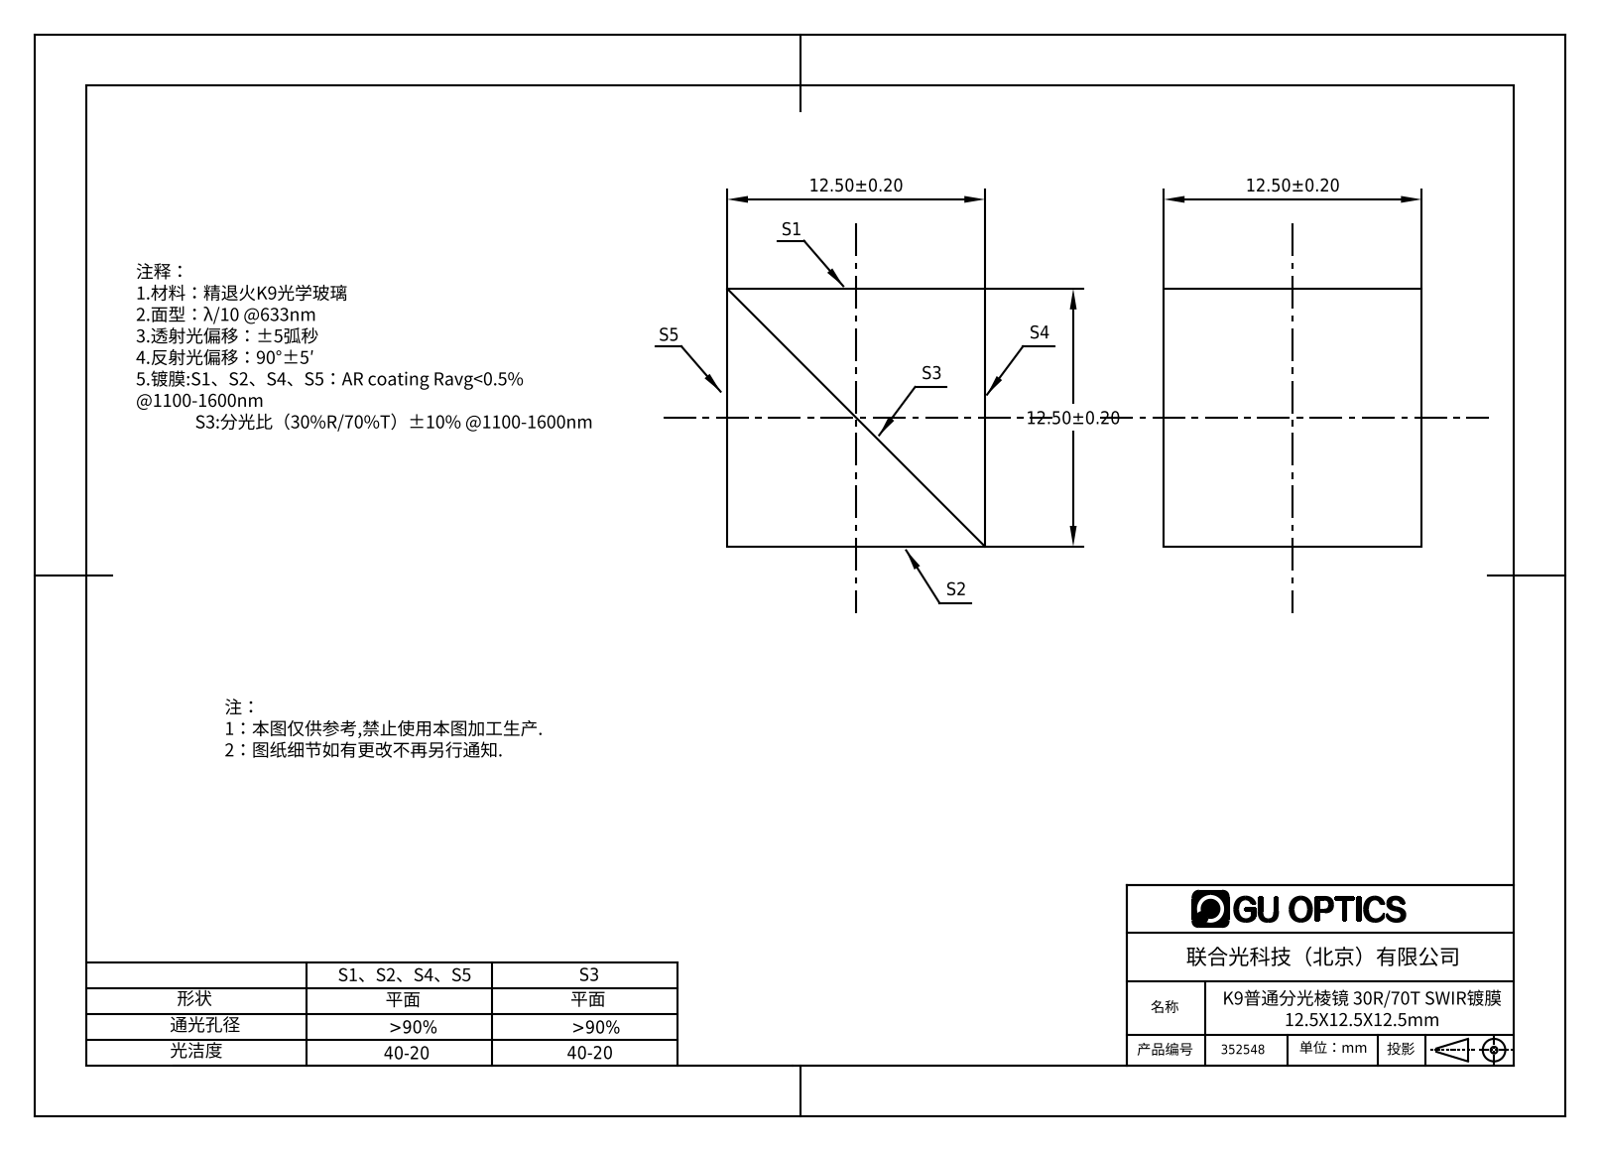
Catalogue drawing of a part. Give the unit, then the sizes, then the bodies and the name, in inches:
Units: inches
Overall size (bounding box): 0.492 × 0.492 × 0.492
Main face-to-face distances: 0.492
Volume: 0.119 in³ · Surface area: 2.137 in²
Bodies: 2 solids, 10 faces (10 planar, 0 cylindrical, 0 other)
Part name (STEP PRODUCT): 352506
STEP written by: SolidWorks 2016 (AUTOMOTIVE_DESIGN)
